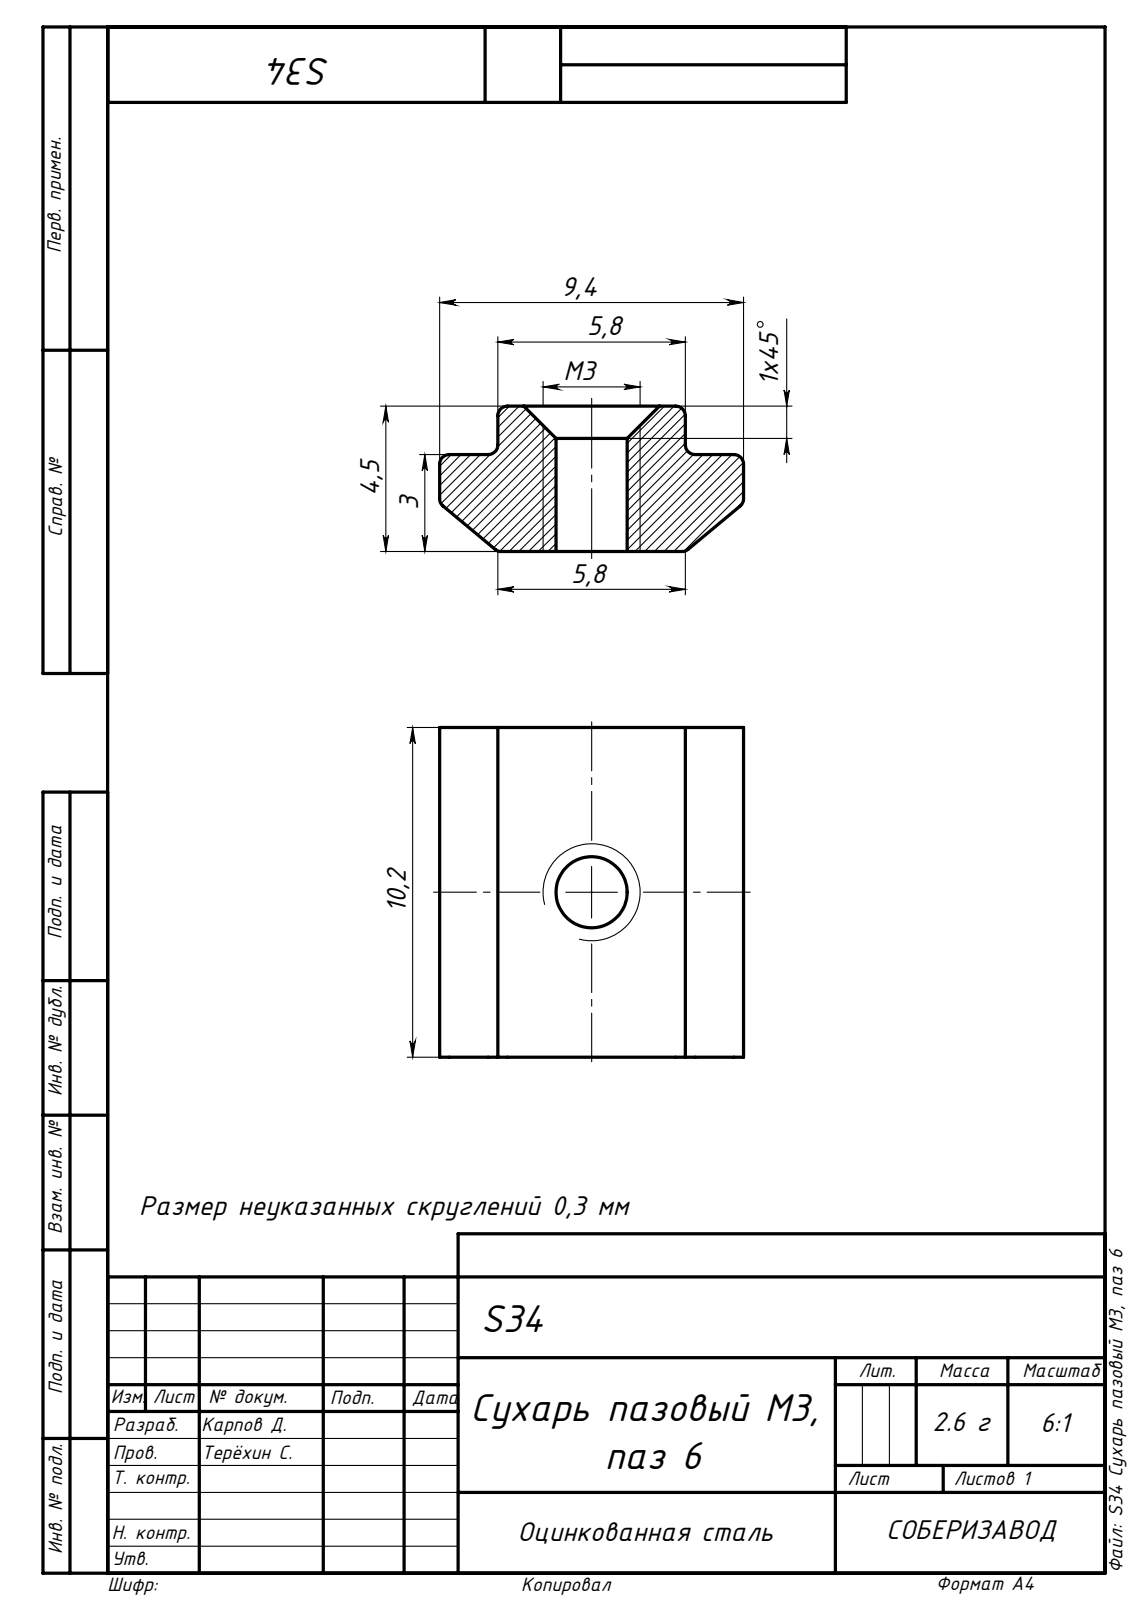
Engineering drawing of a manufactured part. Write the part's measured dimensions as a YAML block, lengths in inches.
part_name: "S34 Сухарь пазовый М3, паз 6"
step_written_by: "SolidWorks 2019 (AUTOMOTIVE_DESIGN)"
units: inches
bodies: {solids: 1, faces: 26, planar: 12, cylindrical: 12, other: 2}
overall_size: [0.402, 0.37, 0.177]
volume: 0.02
surface_area: 0.535
round_holes:
  - {diameter: 0.087, count: 1}
partial_cylinders:
  - {radius: 0.012, count: 10}
face_to_face_distances: [0.177, 0.402, 0.118, 0.059, 0.071, 0.299, 0.37, 0.228]
